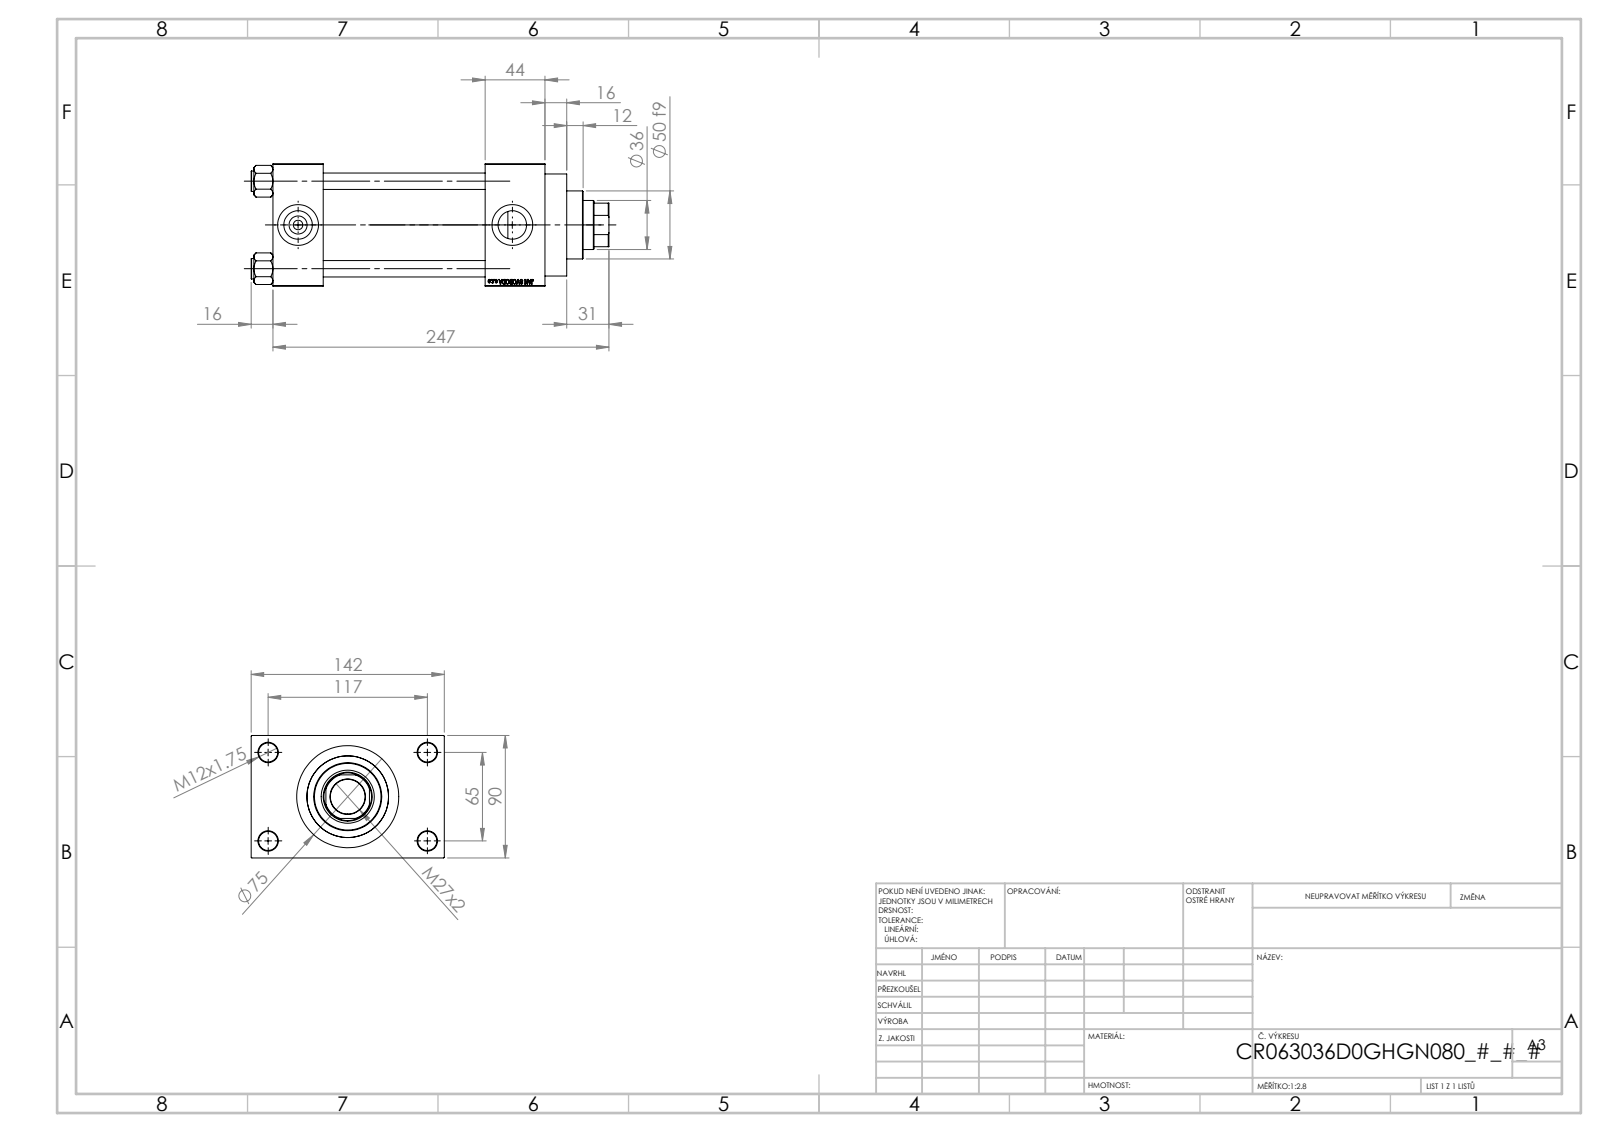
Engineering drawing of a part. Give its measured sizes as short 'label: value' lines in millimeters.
name: V215CR_D_Body; NUT_M5_D; V215CR_D_TYCINKA; V215CR_VCP_D (+1 more)
written by: SolidWorks 2019 (CONFIG_CONTROL_DESIGN)
unit: mm
bodies: 11 solids, 1103 faces (497 planar, 88 cylindrical, 518 other)
size: 263 × 142 × 90
volume: 1 237 000 mm³; area: 246 499 mm²
holes: 4× ⌀12, 4× ⌀14, 2× ⌀7, 2× ⌀20.96, 2× ⌀30, 1× ⌀25.5, 1× ⌀36, 1× ⌀39, 1× ⌀50, 1× ⌀60, 1× ⌀63
bosses: 4× ⌀15, 1× ⌀75, 1× ⌀69
rounds: 1× R17.5
face distances: 90, 119, 37, 156, 200, 163, 44, 26, 116, 142
hole spacings: 26.35, 45.47, 64.3, 66.92, 69.81, 90.65, 111.34, 65
